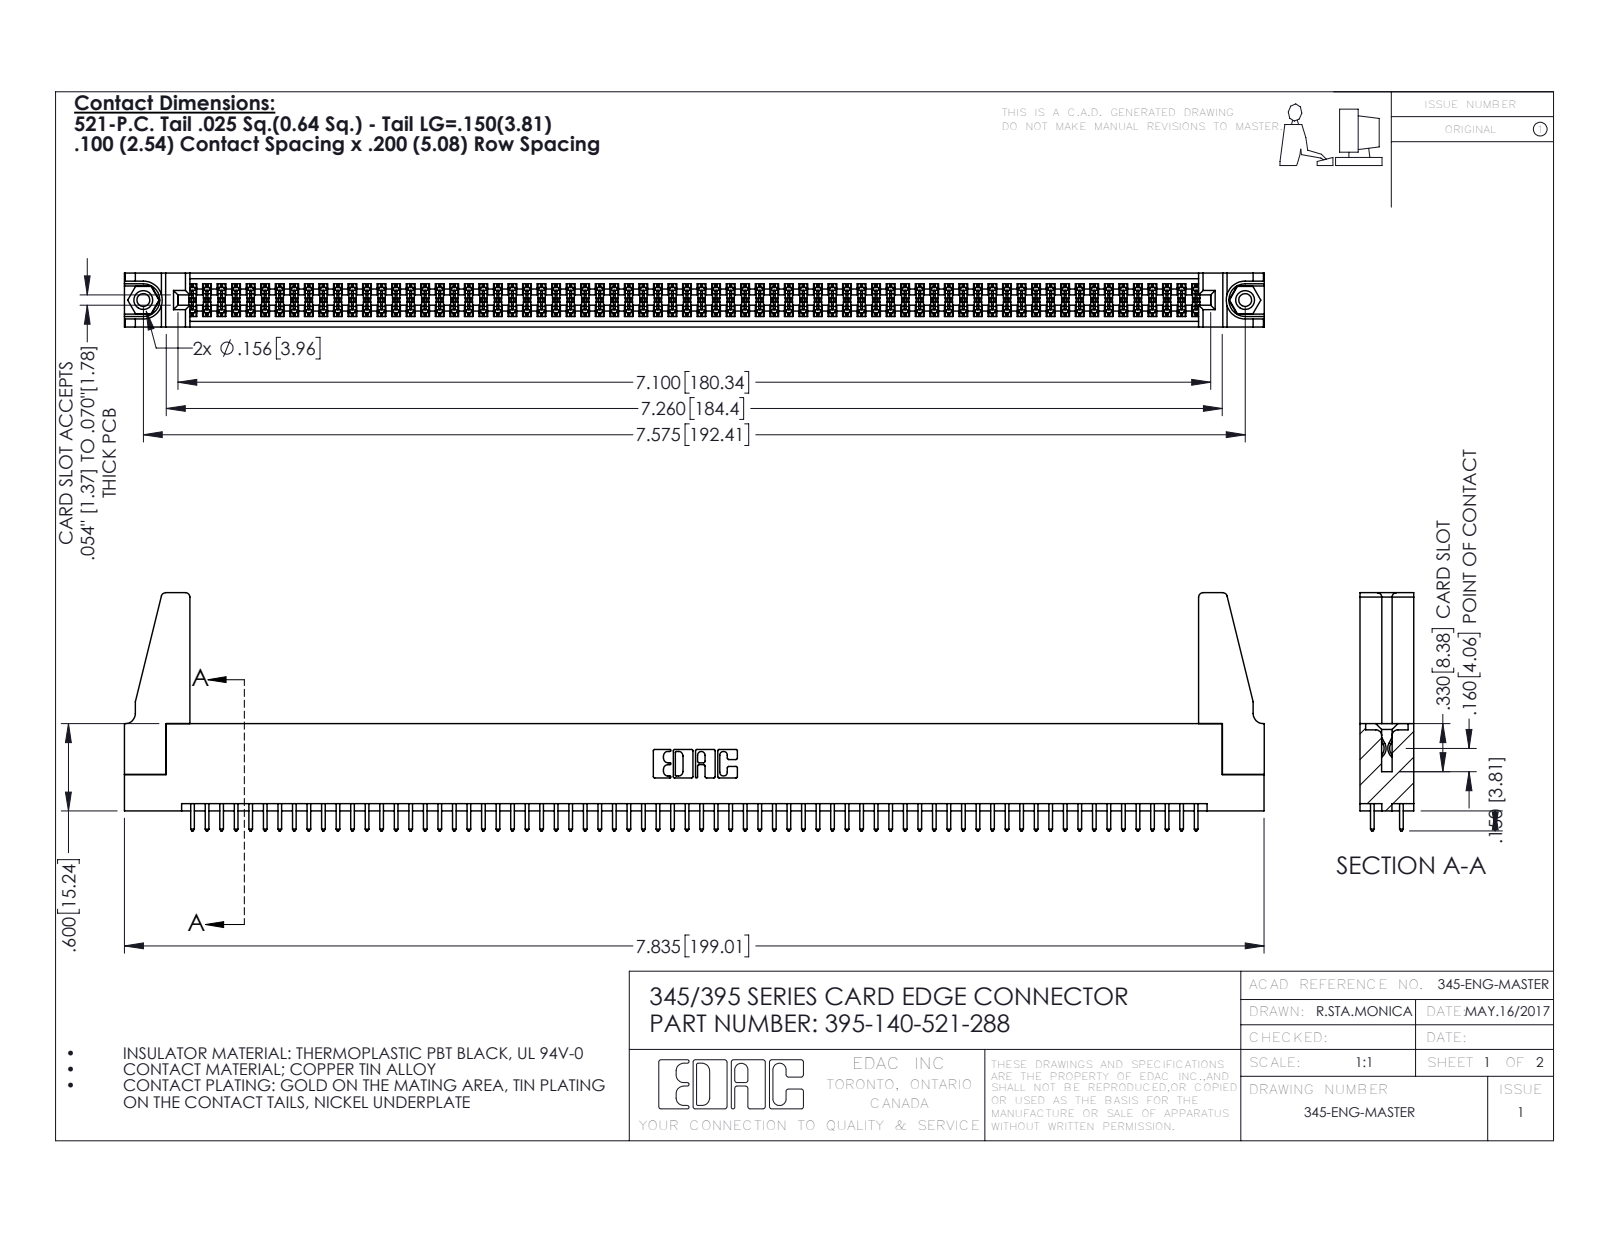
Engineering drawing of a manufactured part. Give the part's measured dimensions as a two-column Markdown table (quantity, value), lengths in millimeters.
| quantity | value |
| --- | --- |
| part name | 345-250-001_345-250-001-102; 395-140-521-288; 345-220-078_345-220-088; 345 Part_Flush Mounting Lugs - 0.156 Dia-TH (+1 more) |
| STEP written by | SolidWorks 2016 (CONFIG_CONTROL_DESIGN) |
| units | millimeters |
| bodies | 145 solids, 7250 faces (4772 planar, 2462 cylindrical, 16 other) |
| overall size | 199 × 41.6 × 9.4 |
| volume | 22 790 mm³ |
| surface area | 32 170 mm² |
| round holes (diameter × count) | 2.3 × 2, 3.2 × 2, 4 × 2, 1.6 × 1 |
| round bosses / shafts (diameter × count) | 3.9 × 2 |
| partial cylindrical surfaces (radius × count) | 0.2 × 210, 0.3 × 140, 0.3 × 22, 0.8 × 8, 0.2 × 6, 0.8 × 6, 0.7 × 3, 0.4 × 2 |
| main face-to-face distances | 1.8, 7.6, 9.4, 5.1, 2.5, 6.9, 0.6, 5.7, 4.4, 3.8 |
| hole center spacings | 6.9, 186.4, 192.4 |
